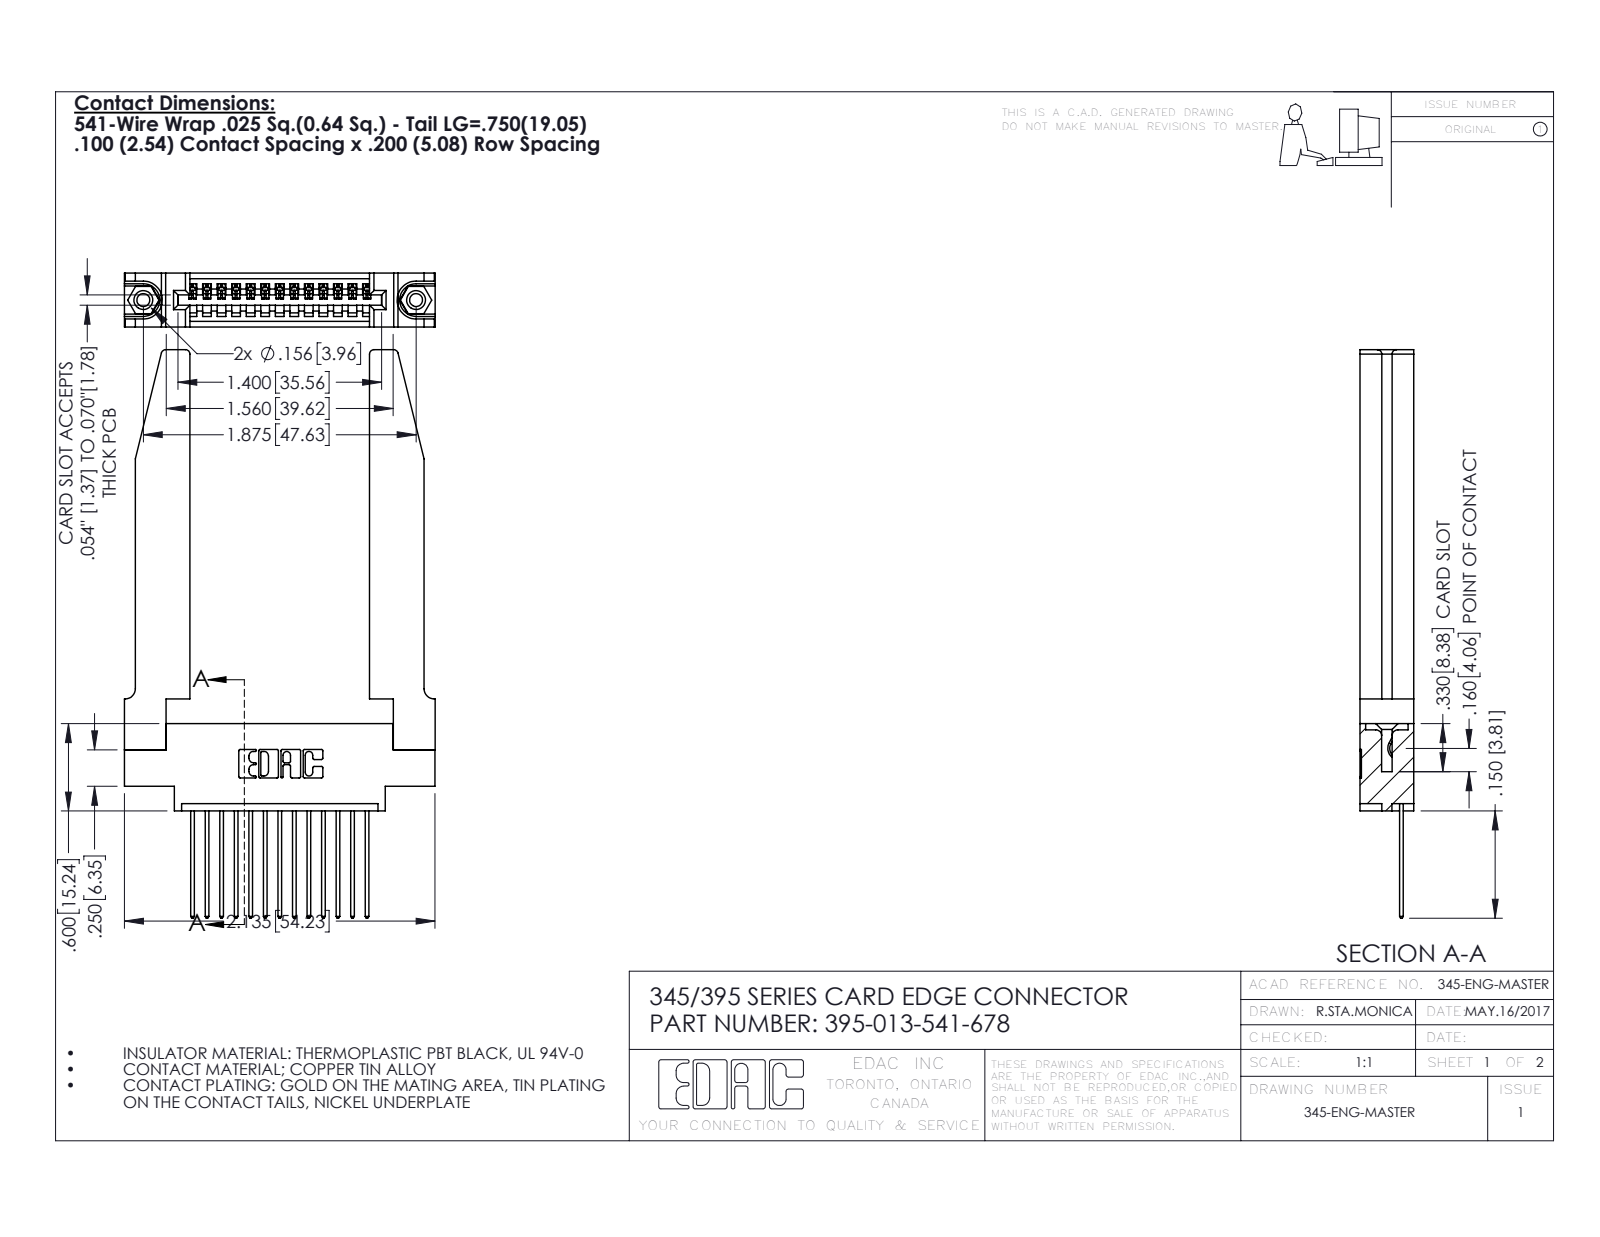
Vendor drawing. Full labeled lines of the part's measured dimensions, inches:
Part name (STEP PRODUCT): 345 Part_0.170 Offset - 0.156 Dia-TH; 345-220-078_345-220-078; 395-013-541-678; 345-250-001_345-250-001-102 (+1 more)
STEP written by: SolidWorks 2016 (CONFIG_CONTROL_DESIGN)
Units: inches
Bodies: 18 solids, 1118 faces (746 planar, 320 cylindrical, 52 other)
Overall size (bounding box): 3.907 × 2.136 × 0.37
Volume: 0.77 in³ · Surface area: 20.57 in²
Round holes (diameter × count): ⌀0.089 ×2, ⌀0.125 ×2, ⌀0.156 ×2, ⌀0.064 ×1
Round bosses / shafts (diameter × count): ⌀0.155 ×2
Partial cylindrical surfaces — rounded edges, fillets, slot ends (radius × count): R0.006 ×26, R0.01 ×26, R0.01 ×22, R0.03 ×8, R0.007 ×6, R0.031 ×6, R0.026 ×3, R0.031 ×2
Main face-to-face distances: 0.37, 0.072, 0.298, 0.148, 0.15, 0.098, 0.272, 0.025, 0.22, 0.077
Hole centre spacings: 0.27, 1.643, 1.875
